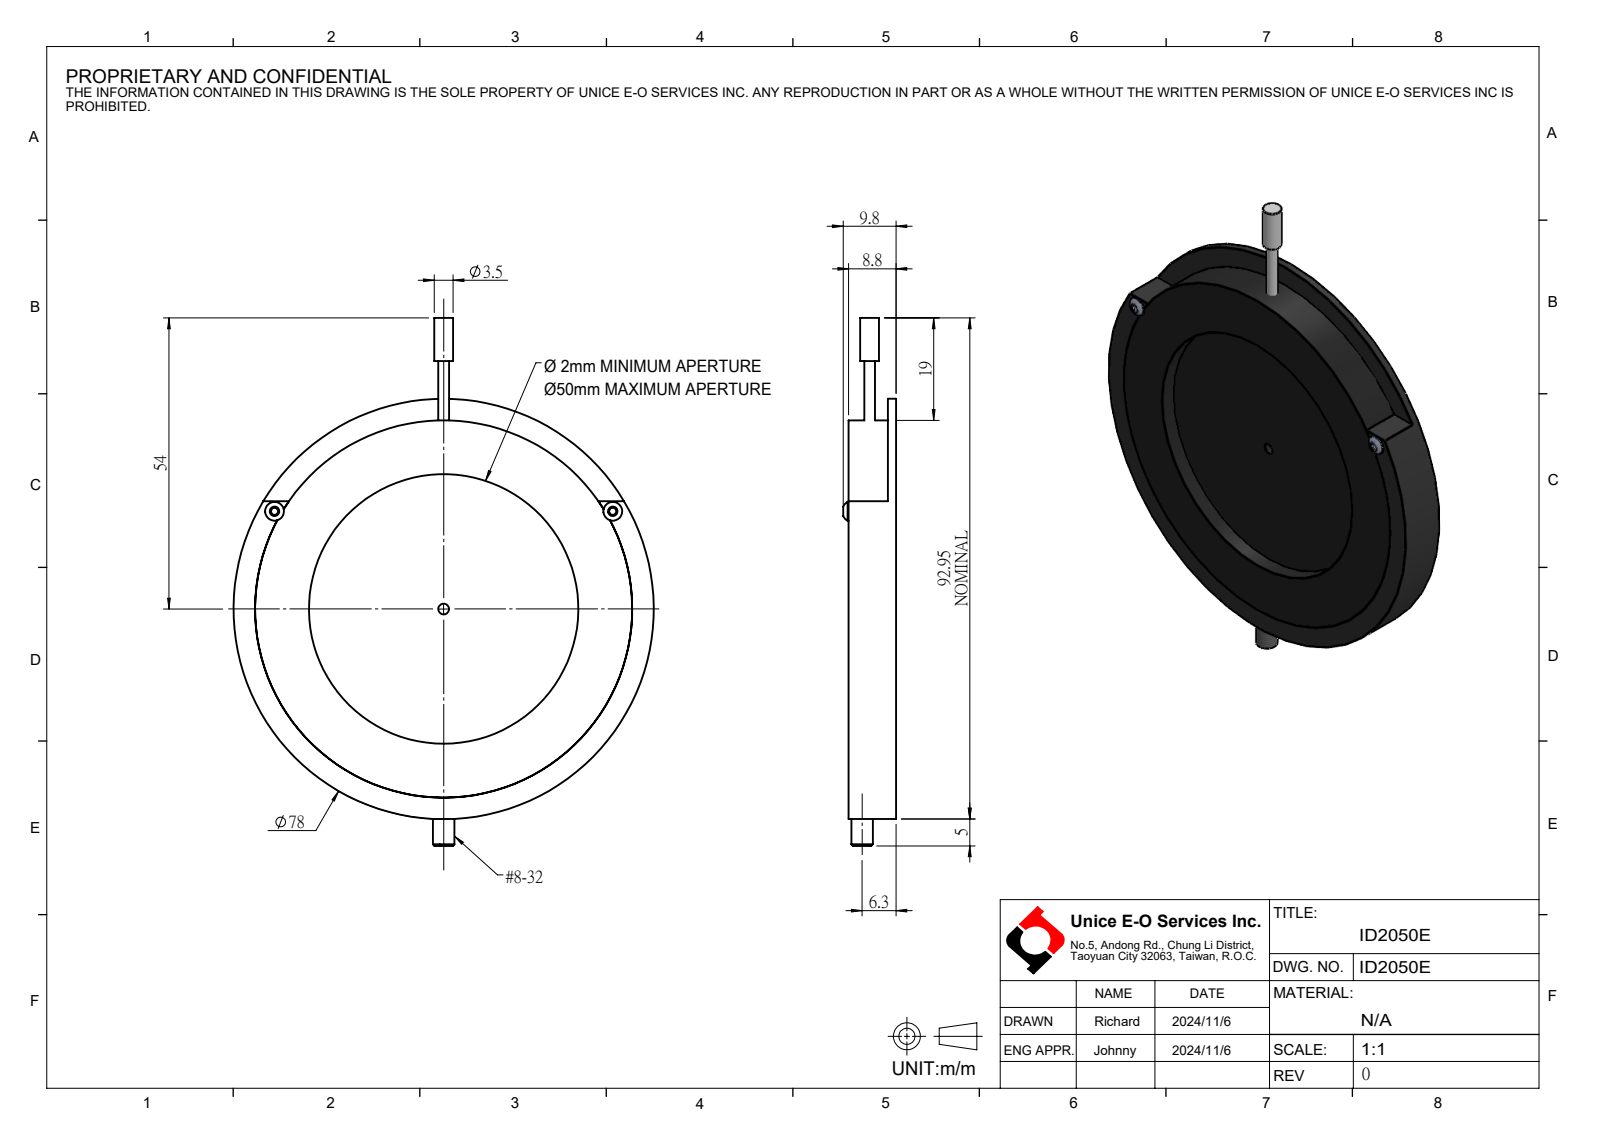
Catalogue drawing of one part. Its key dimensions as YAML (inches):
part_name: "U-F3-B5-M2X6; U-F3-E2-M4x8_U-F3-E1-M5x6; ID2050E; ID2050 (+1 more)"
step_written_by: "SolidWorks 2024 (AUTOMOTIVE_DESIGN)"
units: inches
bodies: {solids: 6, faces: 91, planar: 44, cylindrical: 35, other: 12}
overall_size: [3.856, 3.071, 0.386]
volume: 1.512
surface_area: 25.53
round_holes:
  - {diameter: 0.063, count: 2}
  - {diameter: 0.079, count: 1}
  - {diameter: 0.136, count: 1}
  - {diameter: 1.969, count: 1}
  - {diameter: 2.638, count: 1}
  - {diameter: 2.756, count: 1}
round_bosses_or_shafts:
  - {diameter: 0.138, count: 3}
  - {diameter: 0.079, count: 3}
  - {diameter: 3.071, count: 1}
  - {diameter: 0.157, count: 1}
face_to_face_distances: [0.118, 0.189, 0.307, 0.071, 0.039, 0.157, 0.228, 0.346, 0.059, 0.02]
hole_center_spacings: [1.427, 2.472]
